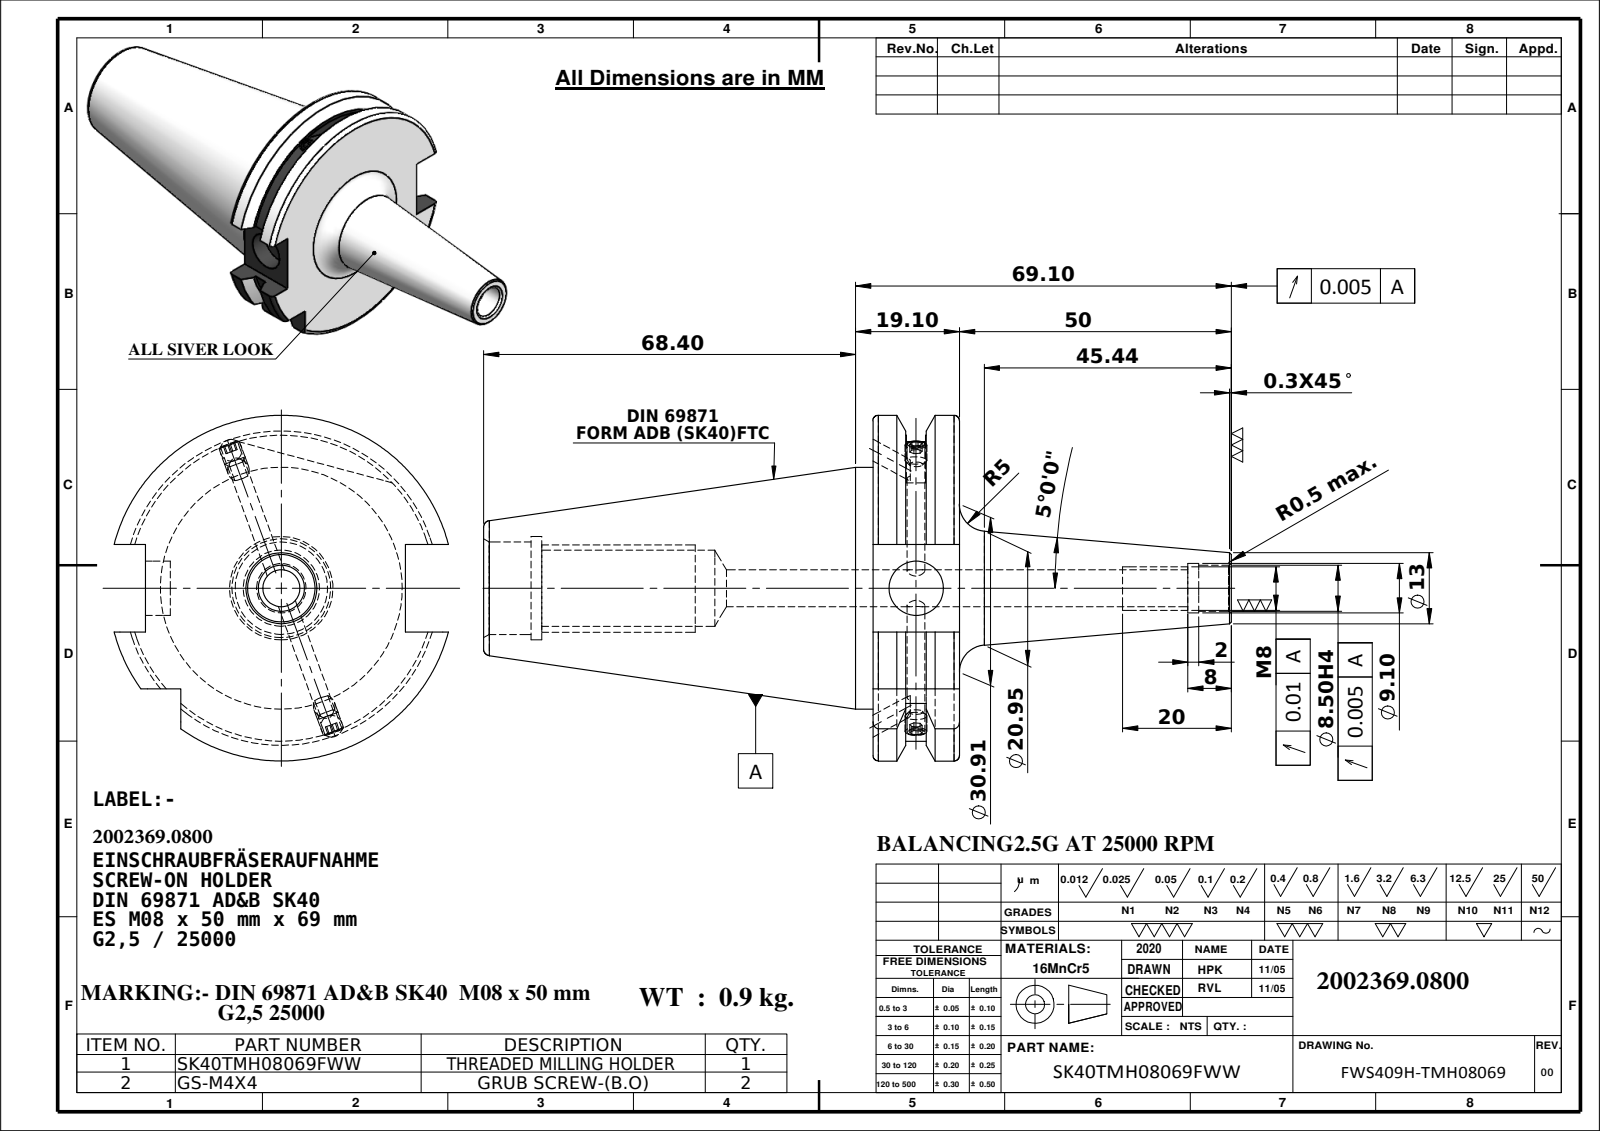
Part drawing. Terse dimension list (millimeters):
name: SK40TMH08069FWW
written by: SolidWorks 2018 (CONFIG_CONTROL_DESIGN)
unit: mm
bodies: 1 solid, 98 faces (30 planar, 32 cylindrical, 36 other)
size: 137.5 × 63.55 × 61.48
volume: 113 849 mm³; area: 24 040 mm²
holes: 1× ⌀3.3, 1× ⌀6.8, 1× ⌀8.5, 1× ⌀9.1, 1× ⌀10, 1× ⌀14, 1× ⌀17, 1× ⌀19
bosses: 1× ⌀44.45
rounds: 1× R28.12, 1× R31.77
face distances: 15.9, 16.1, 47.8, 3.62, 71.6, 87.5, 10.7, 60.9, 76.8, 77.63
